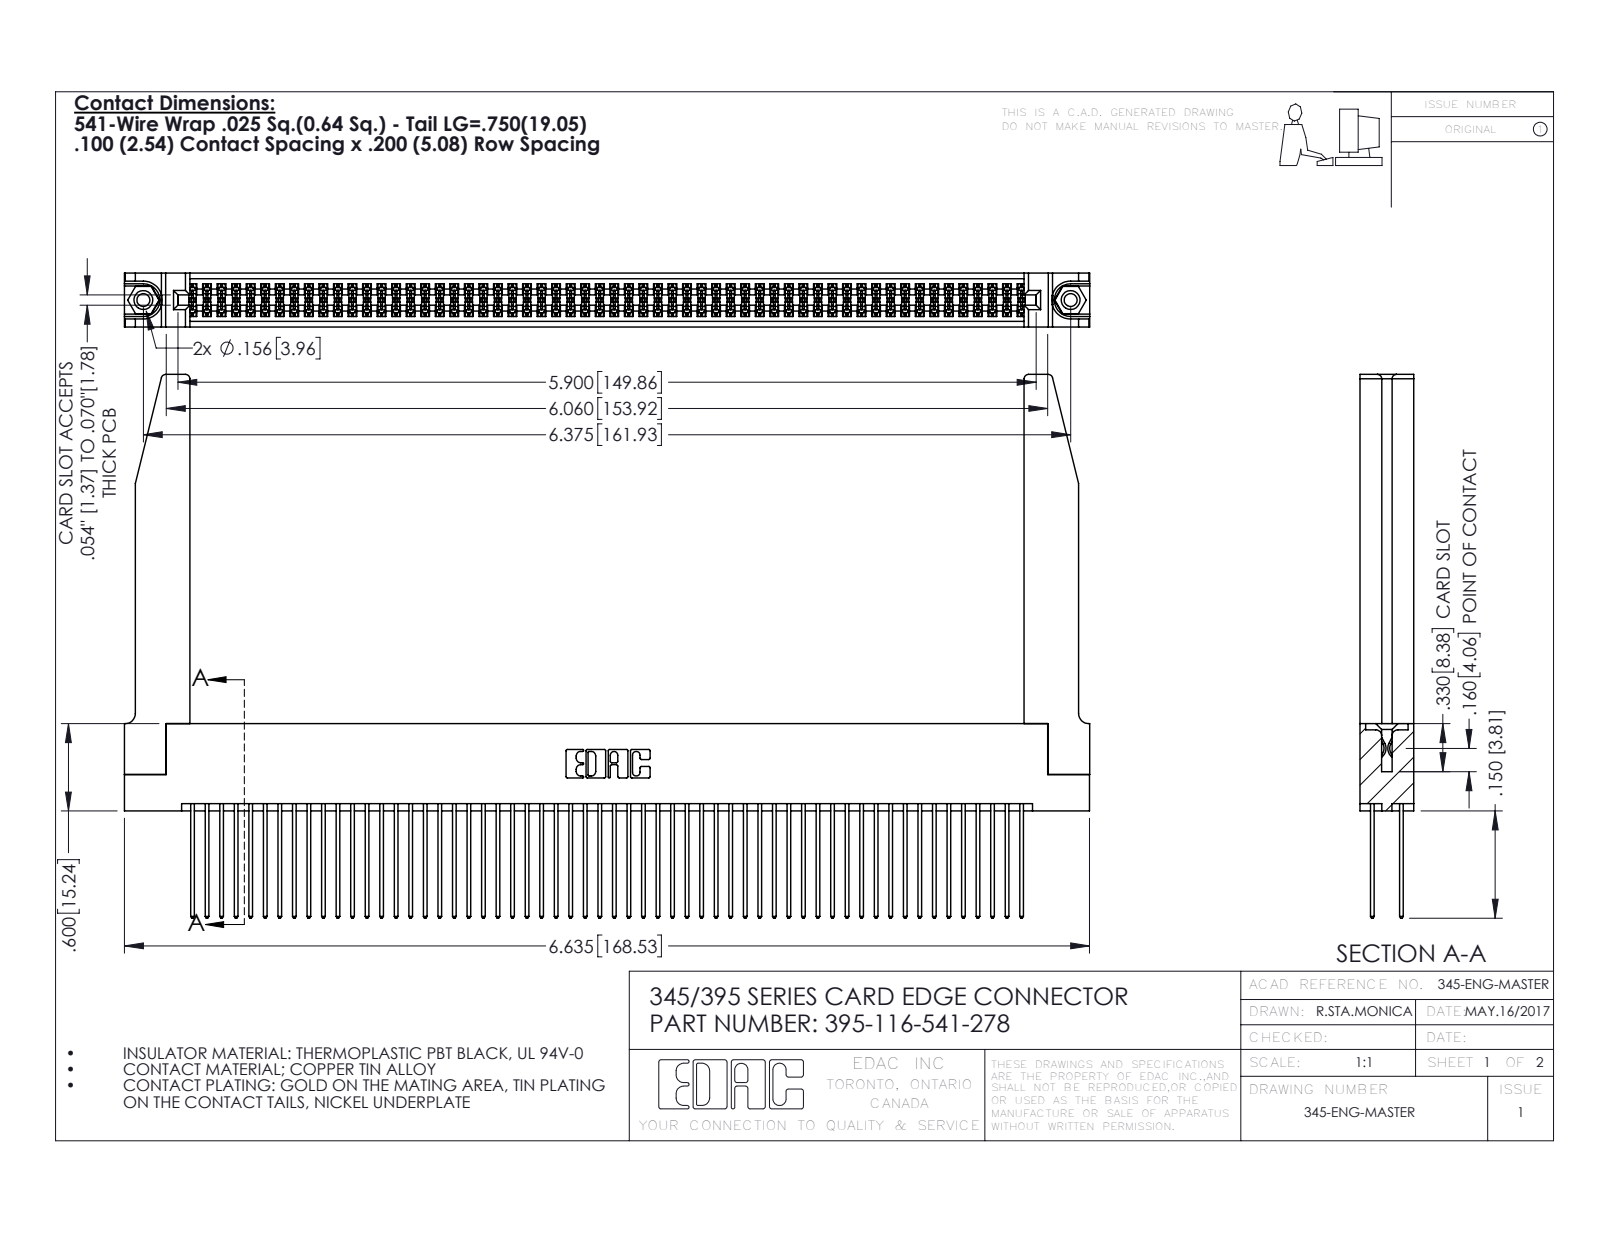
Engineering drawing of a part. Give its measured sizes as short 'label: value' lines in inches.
name: 345 Part_Flush Mounting Lugs - 0.156 Dia-TH; 395-116-541-278; 345-292-001_345-293-141; 345-250-001_345-250-001-102 (+1 more)
written by: SolidWorks 2016 (CONFIG_CONTROL_DESIGN)
unit: in
bodies: 121 solids, 6160 faces (4050 planar, 2058 cylindrical, 52 other)
size: 6.636 × 3.737 × 0.37
volume: 1.523 in³; area: 55.31 in²
holes: 2× ⌀0.089, 2× ⌀0.125, 2× ⌀0.156, 1× ⌀0.064
bosses: 2× ⌀0.155
rounds: 174× R0.006, 116× R0.01, 22× R0.01, 8× R0.03, 6× R0.007, 6× R0.031, 3× R0.026, 2× R0.014
face distances: 0.072, 0.298, 0.2, 0.37, 0.098, 0.272, 0.025, 0.225, 0.175, 0.15
hole spacings: 0.27, 6.139, 6.375
